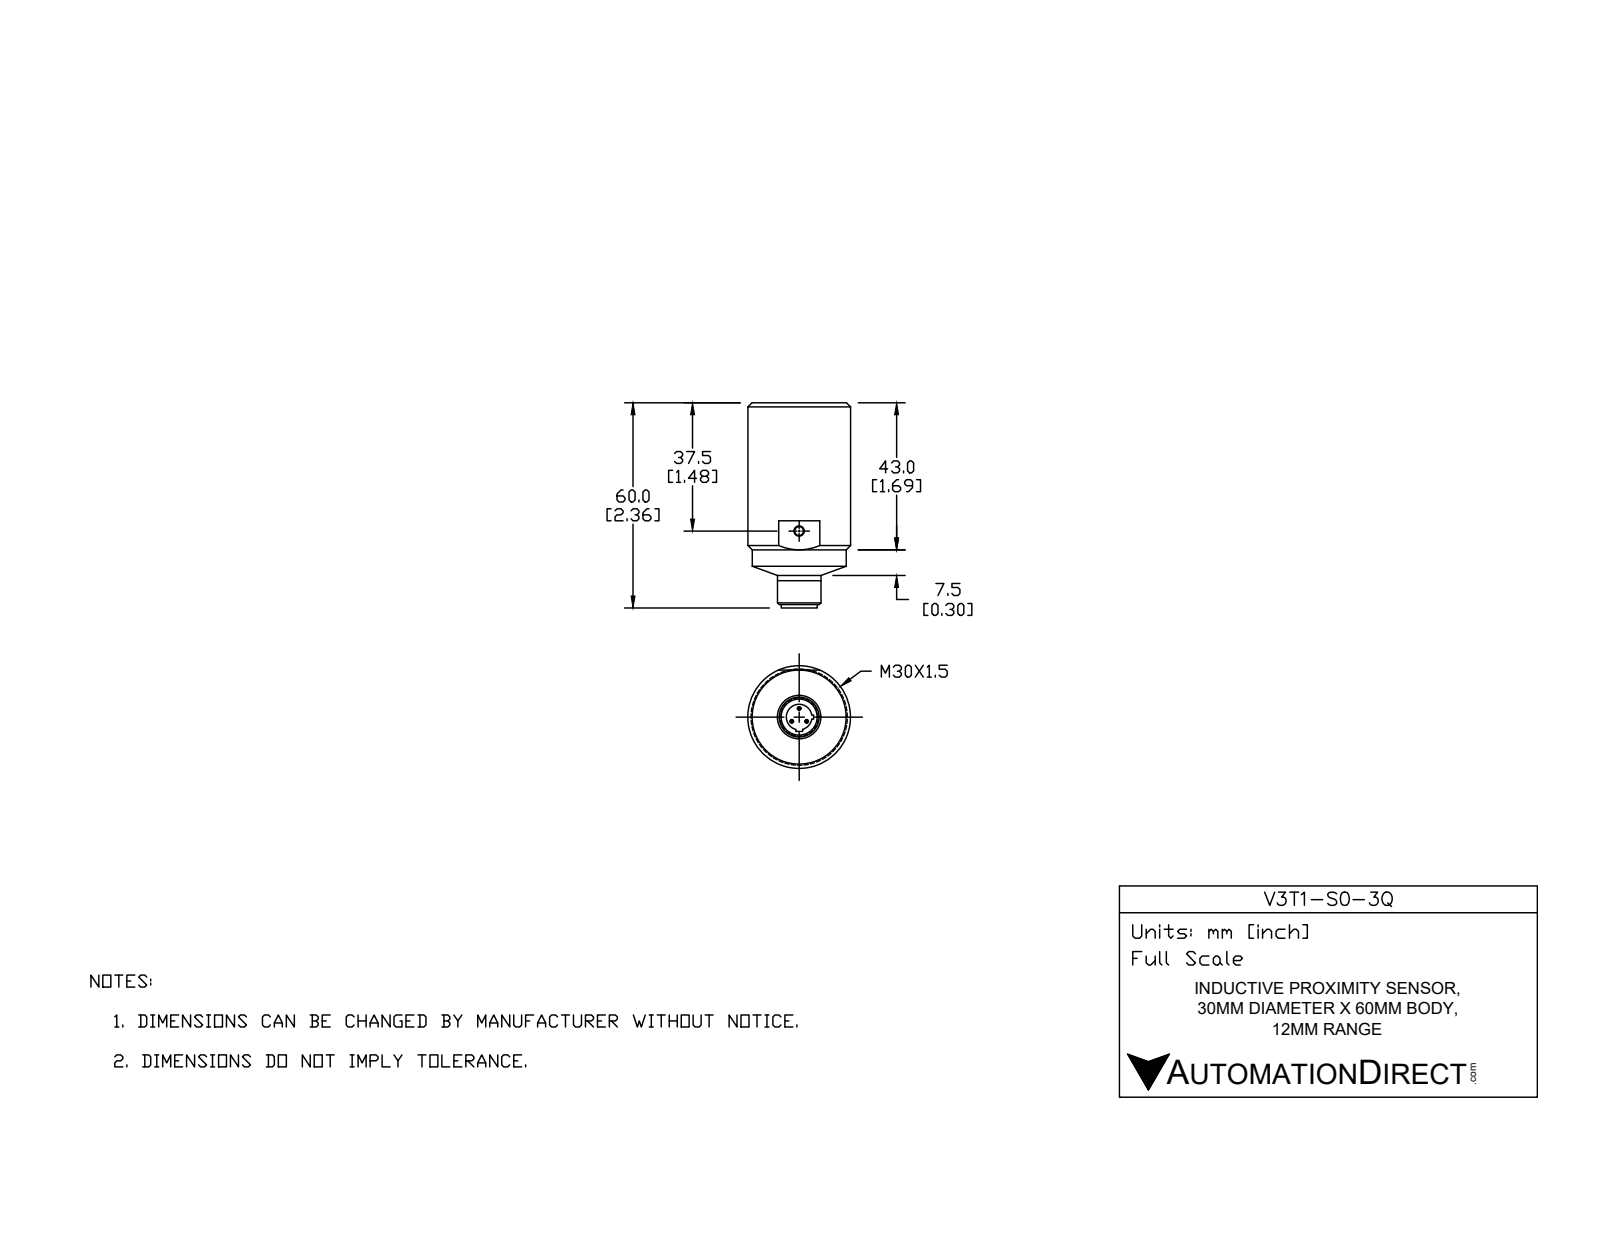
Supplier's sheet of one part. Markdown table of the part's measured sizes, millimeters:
| quantity | value |
| --- | --- |
| part name | V3T1_3Q_fig |
| STEP written by | ST-DEVELOPER v16.7 (AUTOMOTIVE_DESIGN) |
| units | millimeters |
| bodies | 3 solids, 55 faces (25 planar, 20 cylindrical, 10 other) |
| overall size | 60 × 30 × 30 |
| volume | 34 721 mm³ |
| surface area | 7 192 mm² |
| round holes (diameter × count) | 1 × 3, 2.6 × 1, 7.5 × 1, 9.5 × 1, 26 × 1 |
| round bosses / shafts (diameter × count) | 0.98 × 3, 30 × 1, 27.5 × 1, 25.75 × 1, 12.7 × 1, 10.5 × 1, 9.55 × 1, 9.4 × 1 |
| partial cylindrical surfaces (radius × count) | 12 × 1 |
| main face-to-face distances | 52.9, 60, 7.1, 1, 59, 6.1, 17.95, 3, 49.9, 56 |
| hole center spacings | 2.5, 4.33, 4.34 |
